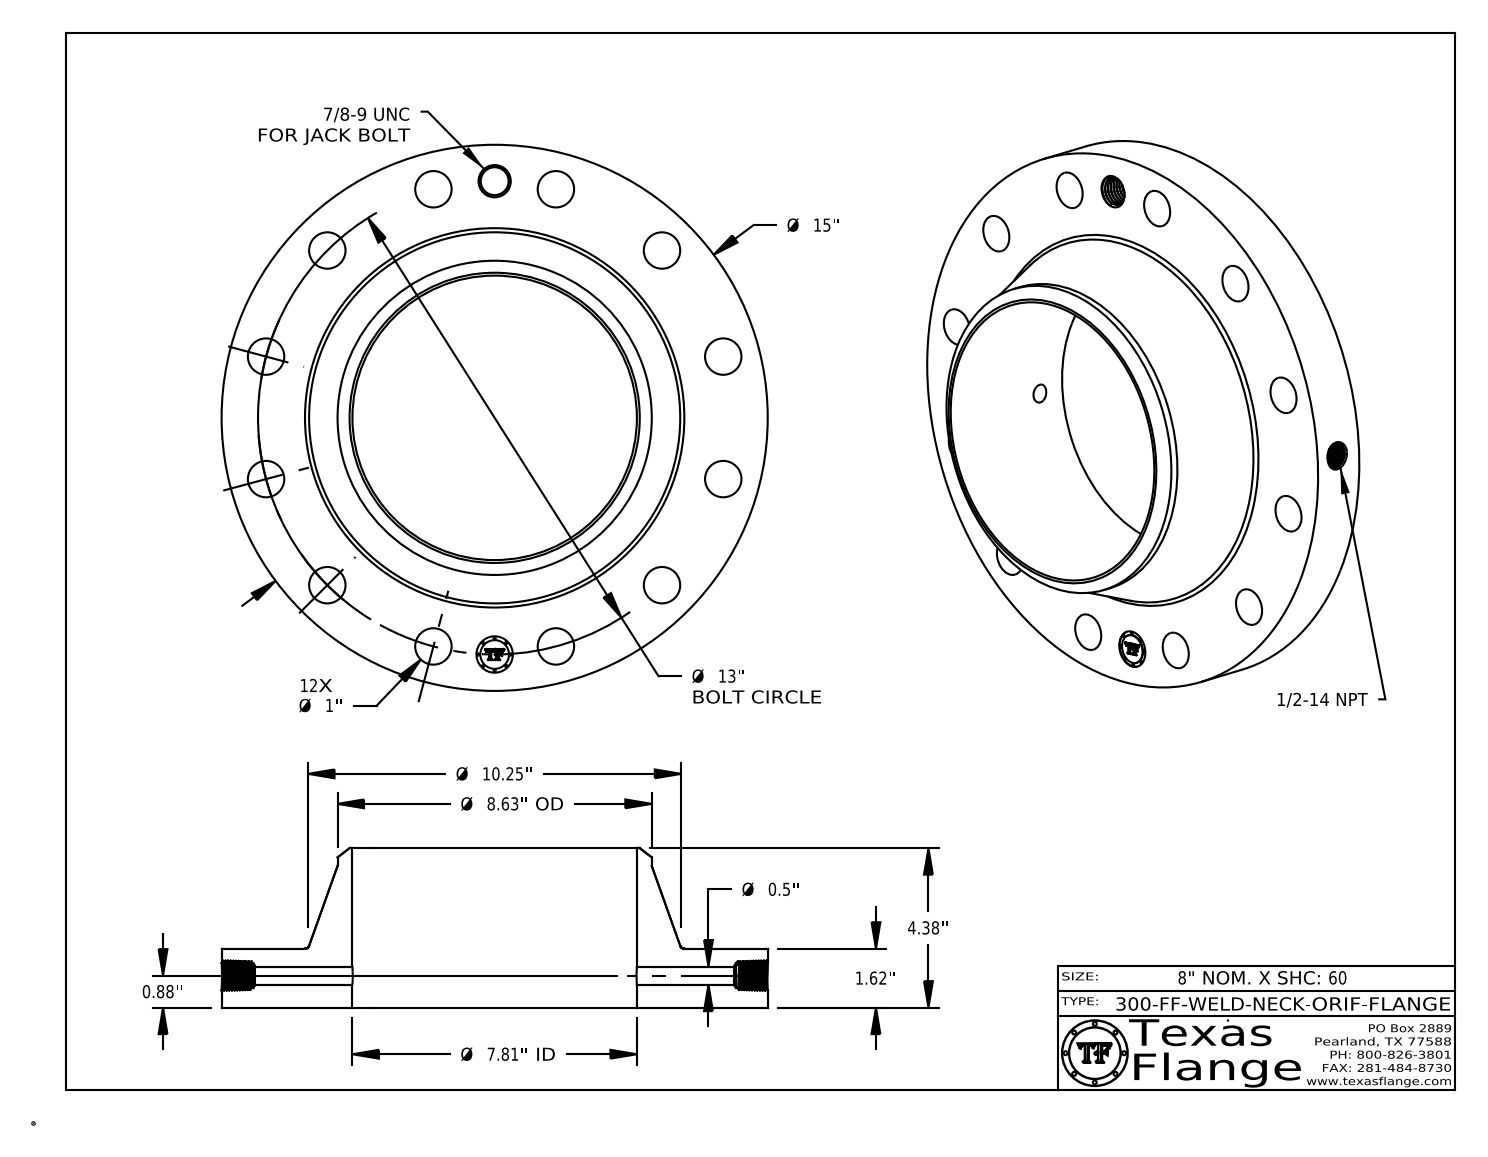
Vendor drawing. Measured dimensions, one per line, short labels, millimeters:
name: 300-FF-WELD-NECK
written by: CATIA V5 STEP AP214 (AUTOMOTIVE_DESIGN)
unit: mm
bodies: 1 solid, 770 faces (368 planar, 98 cylindrical, 304 other)
size: 381 × 381 × 111.3
volume: 4 018 000 mm³; area: 360 400 mm²
holes: 13× ⌀25.4, 1× ⌀12.7, 1× ⌀17.1, 1× ⌀19.5, 1× ⌀198.5
bosses: 8× ⌀1.5, 1× ⌀381, 1× ⌀219.2, 1× ⌀20
face distances: 41.1, 111.3, 70.1, 40.8, 0.4, 70.5, 7.6, 7.4, 1.4, 6.3
hole spacings: 165.1, 85.5, 233.5, 286, 318.9, 330.2, 43.1, 126.4
